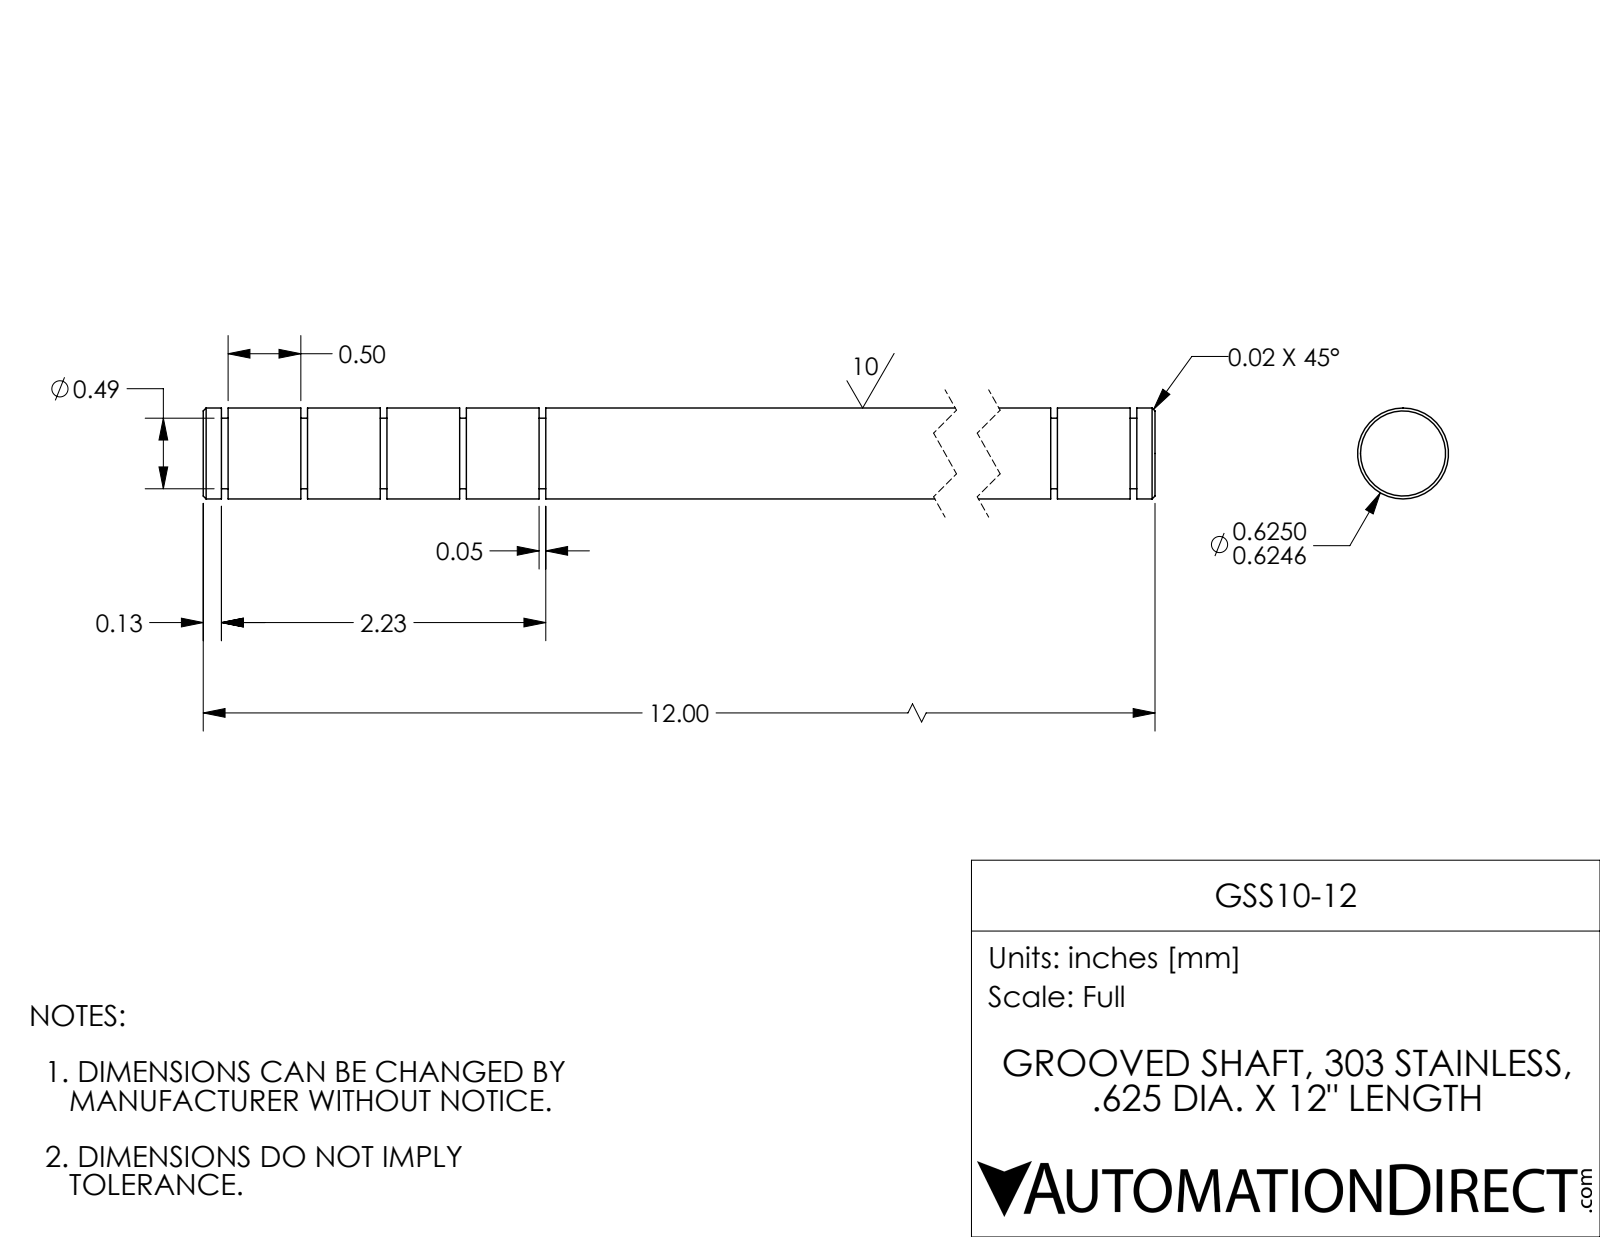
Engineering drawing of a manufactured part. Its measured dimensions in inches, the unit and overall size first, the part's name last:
Units: inches
Overall size (bounding box): 12 × 0.625 × 0.625
Round bosses / shafts (diameter × count): ⌀0.625 ×1, ⌀0.485 ×1
Main face-to-face distances: 0.546, 0.046, 1.092, 0.5, 0.592, 1.638, 1.138, 11.158, 1.046, 10.612
Volume: 3.641 in³ · Surface area: 25.7 in²
Bodies: 1 solid, 50 faces (16 planar, 30 cylindrical, 4 other)
Part name (STEP PRODUCT): GSS10-12
STEP written by: SolidWorks 2017 (AUTOMOTIVE_DESIGN)
